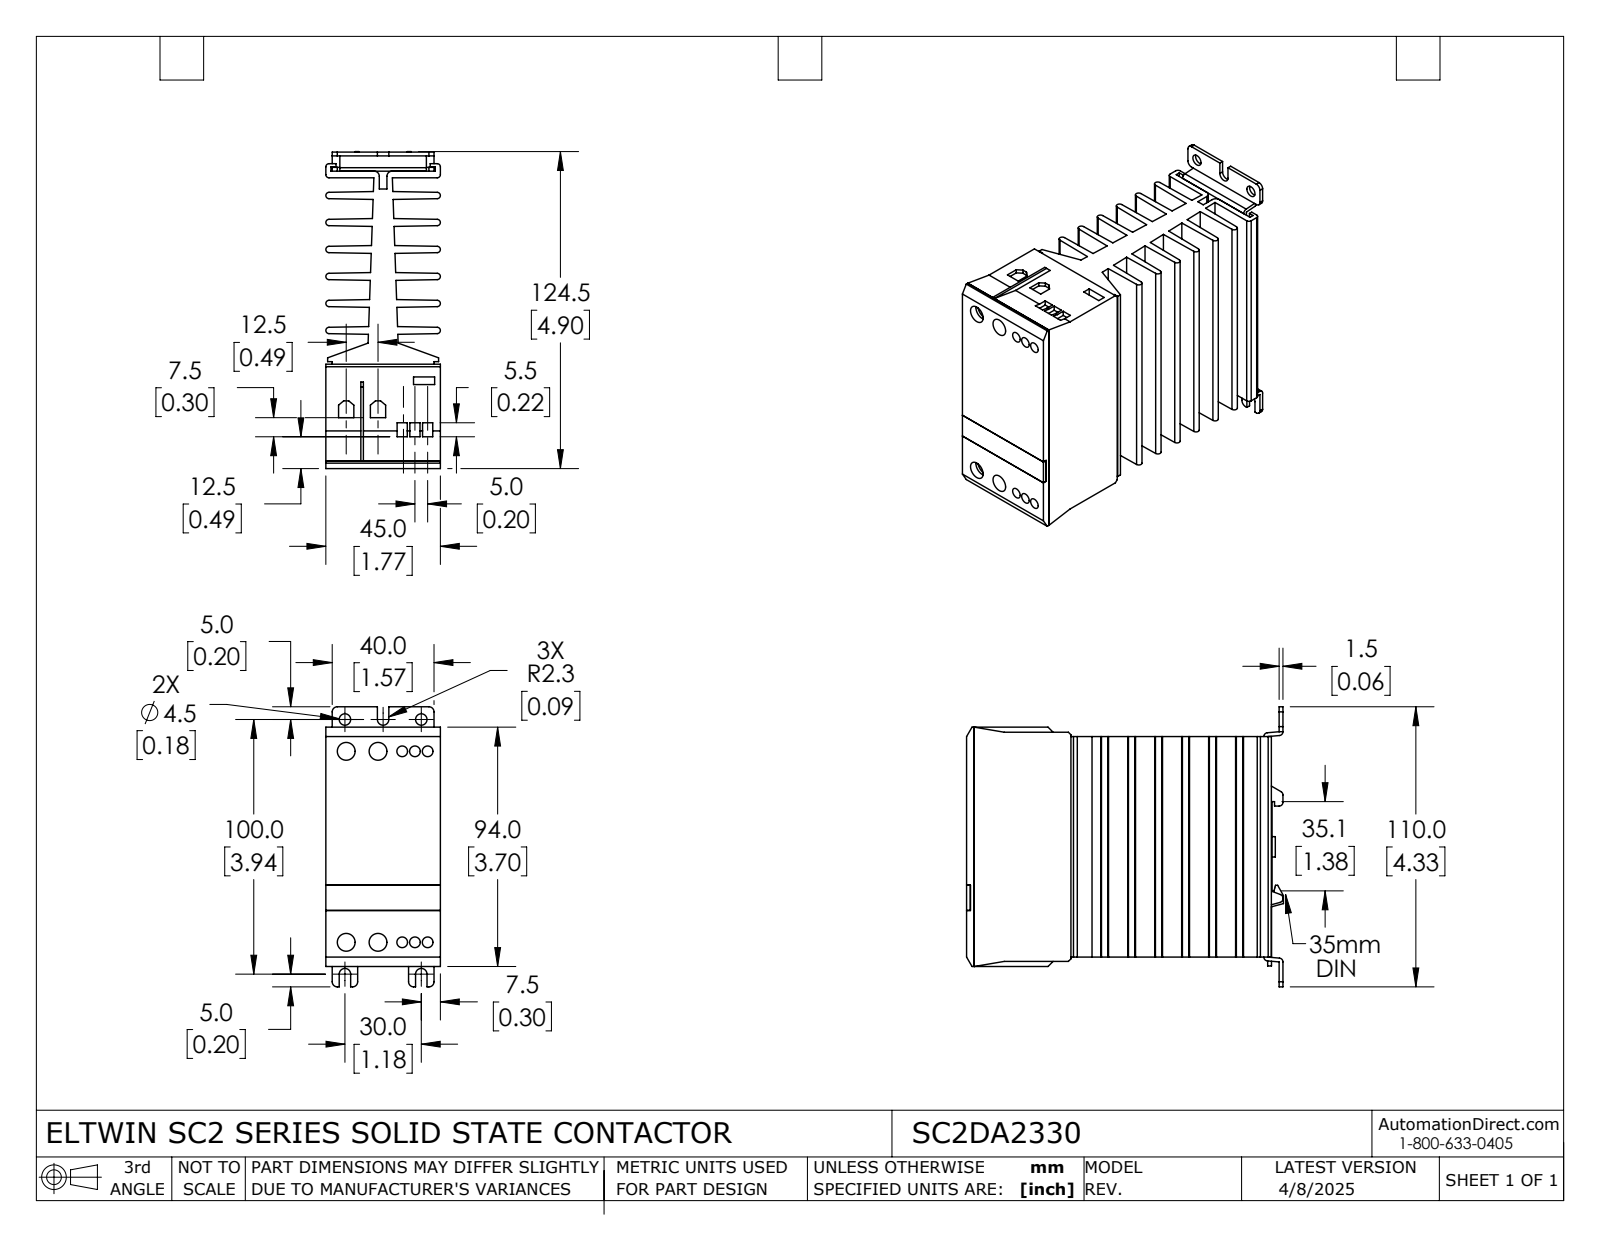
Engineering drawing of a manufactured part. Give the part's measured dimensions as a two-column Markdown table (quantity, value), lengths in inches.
| quantity | value |
| --- | --- |
| part name | SC2DA2330 |
| STEP written by | SolidWorks 2021 (AUTOMOTIVE_DESIGN) |
| units | inches |
| bodies | 7 solids, 391 faces (284 planar, 107 cylindrical, 0 other) |
| overall size | 4.902 × 4.331 × 1.772 |
| volume | 18.87 in³ |
| surface area | 165.4 in² |
| round holes (diameter × count) | 0.165 × 6, 0.173 × 6, 0.276 × 4, 0.177 × 2, 0.315 × 2 |
| round bosses / shafts (diameter × count) | 0.315 × 3 |
| partial cylindrical surfaces (radius × count) | 0.079 × 18, 0.049 × 16, 0.059 × 10, 0.051 × 4, 0.089 × 3 |
| main face-to-face distances | 0.417, 0.835, 0.127, 1.252, 0.29, 0.544, 0.707, 0.962, 1.669, 1.125 |
| hole center spacings | 2.953, 0.197, 2.959, 0.374, 0.394, 0.492, 0.502, 0.571 |
